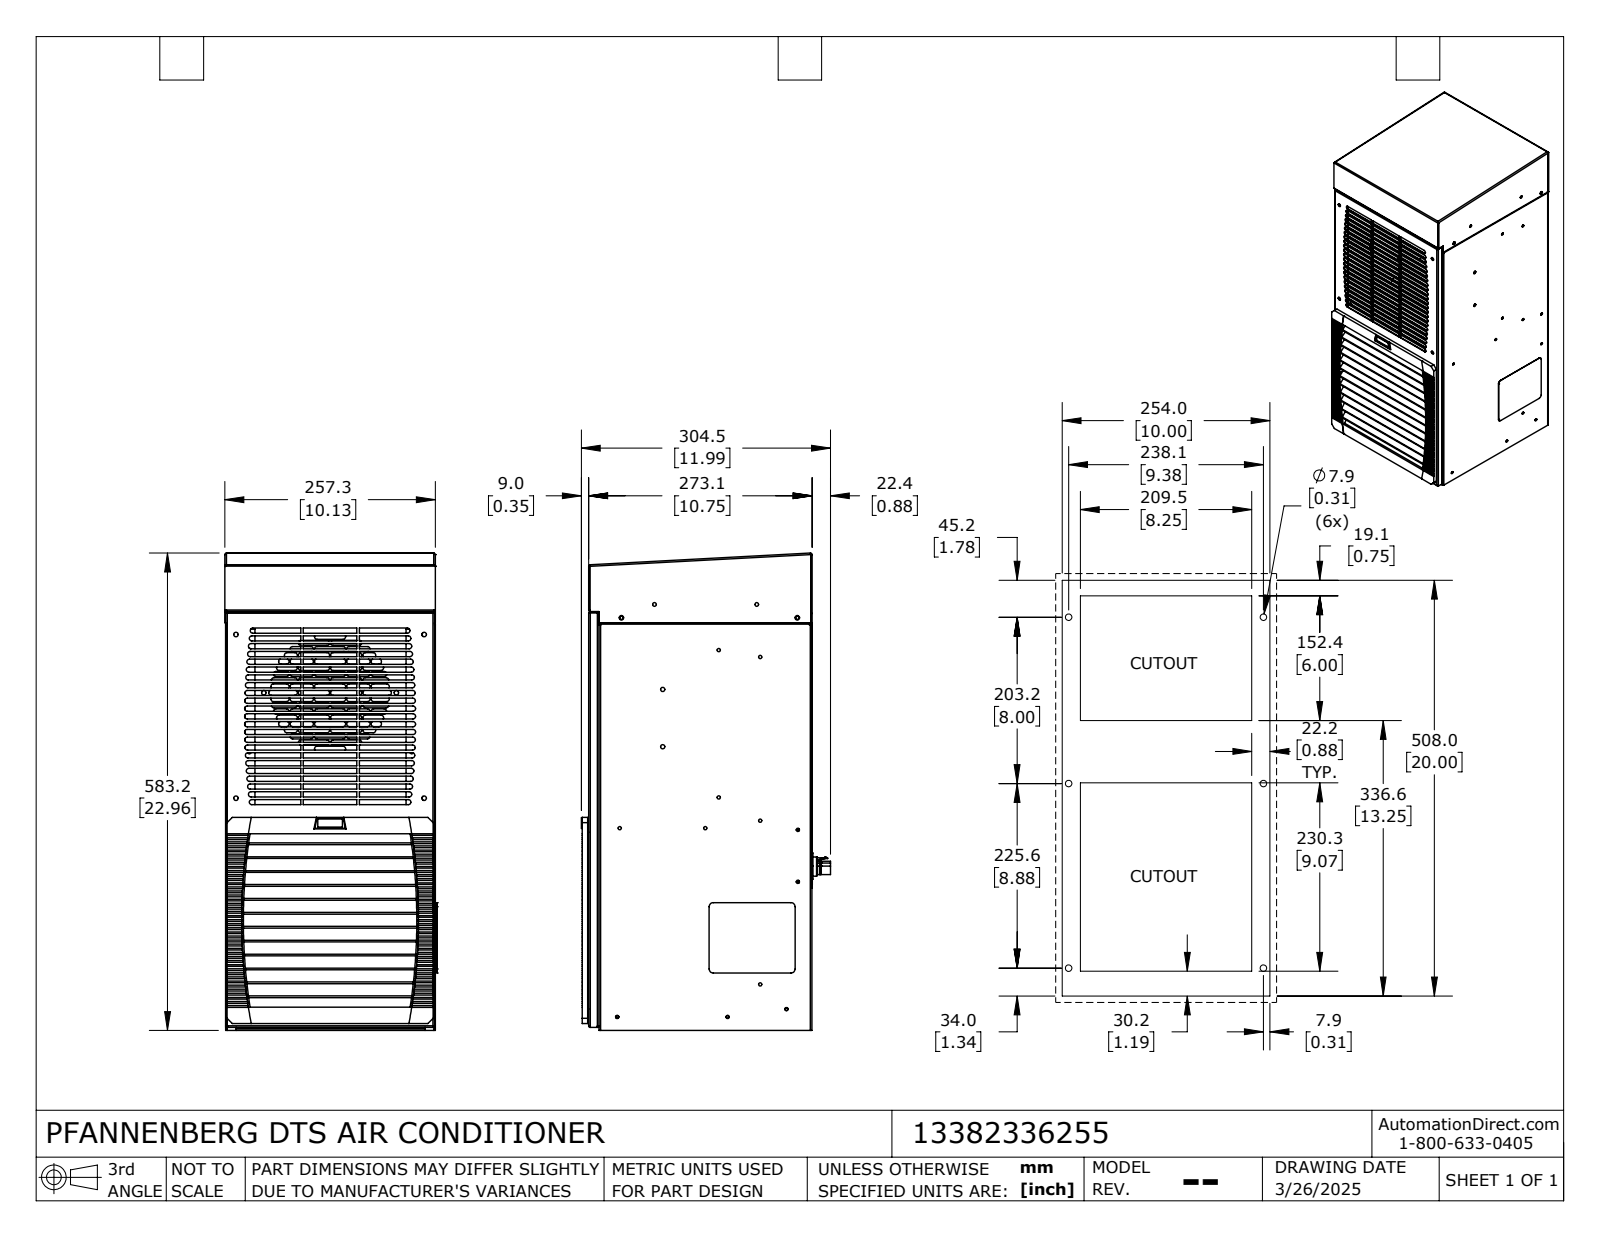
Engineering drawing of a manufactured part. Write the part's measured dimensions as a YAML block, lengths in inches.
part_name: "13382336255_Default"
step_written_by: "SolidWorks 2024 (CONFIG_CONTROL_DESIGN)"
units: inches
bodies: {solids: 11, faces: 2407, planar: 1386, cylindrical: 910, other: 111}
overall_size: [22.962, 11.99, 10.222]
volume: 112.6
surface_area: 2764
round_holes:
  - {diameter: 0.156, count: 12}
  - {diameter: 0.157, count: 12}
  - {diameter: 0.217, count: 12}
  - {diameter: 0.187, count: 8}
  - {diameter: 0.165, count: 6}
  - {diameter: 0.169, count: 5}
  - {diameter: 0.209, count: 5}
  - {diameter: 0.149, count: 4}
  - {diameter: 0.281, count: 4}
  - {diameter: 0.313, count: 4}
  - {diameter: 0.394, count: 4}
  - {diameter: 0.129, count: 3}
round_bosses_or_shafts:
  - {diameter: 0.079, count: 4}
  - {diameter: 1.378, count: 1}
  - {diameter: 1.102, count: 1}
  - {diameter: 0.945, count: 1}
  - {diameter: 0.906, count: 1}
  - {diameter: 0.56, count: 1}
  - {diameter: 0.475, count: 1}
  - {diameter: 0.475, count: 1}
partial_cylinders:
  - {radius: 0.125, count: 186}
  - {radius: 0.118, count: 43}
  - {radius: 0.031, count: 32}
  - {radius: 0.076, count: 32}
  - {radius: 0.049, count: 24}
  - {radius: 0.031, count: 10}
  - {radius: 0.076, count: 10}
  - {radius: 0.079, count: 8}
face_to_face_distances: [0.045, 0.045, 10.006, 10.051, 10.05, 10.096, 10.711, 0.039, 10.045, 0.473]
hole_center_spacings: [7.874, 2.5, 8.381, 13.755, 16.255, 0.045, 1.083, 2.5]
